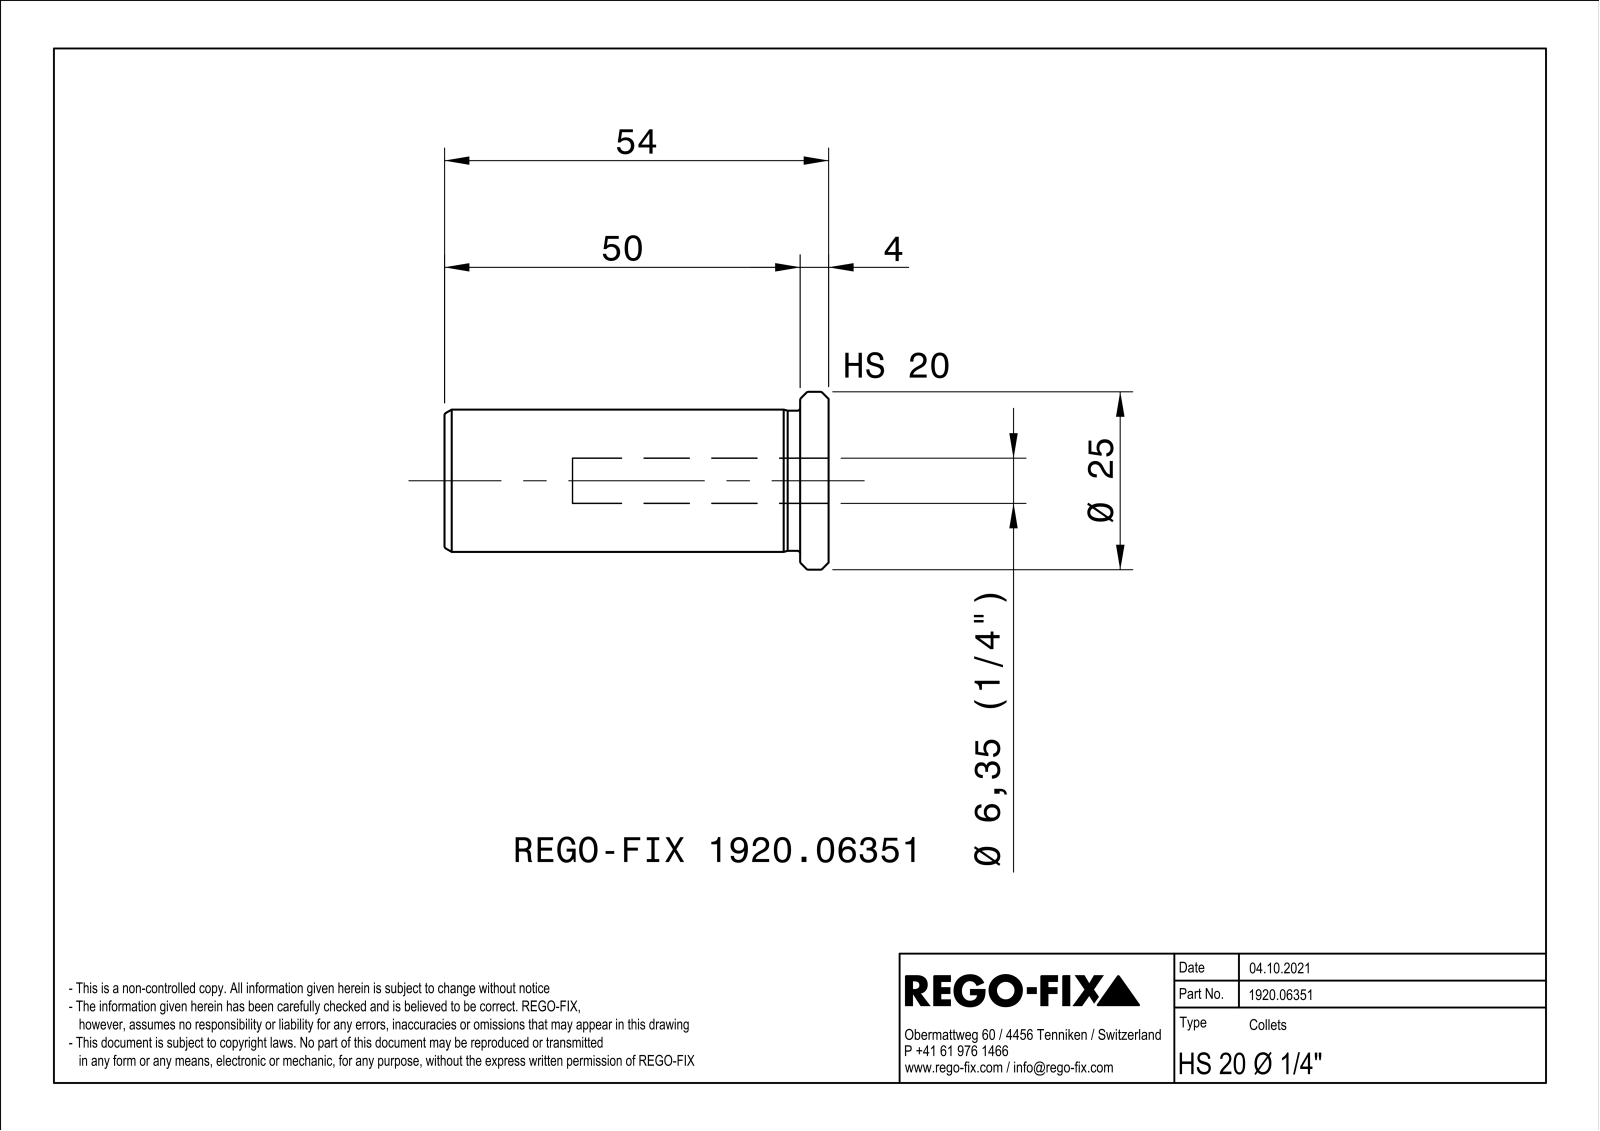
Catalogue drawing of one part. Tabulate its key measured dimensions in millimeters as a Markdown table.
| quantity | value |
| --- | --- |
| part name | NOCUT |
| STEP written by | SIEMENS PLM Software Solid Edge ST10 (AUTOMOTIVE_DESIGN) |
| units | millimeters |
| bodies | 1 solid, 72 faces (22 planar, 12 cylindrical, 38 other) |
| overall size | 54 × 24.98 × 24.98 |
| volume | 12 685 mm³ |
| surface area | 7 034 mm² |
| round holes (diameter × count) | 6.35 × 1, 10 × 1, 16.5 × 1 |
| round bosses / shafts (diameter × count) | 25 × 1, 20 × 1, 19.7 × 1 |
| main face-to-face distances | 1, 4, 54, 50 |
